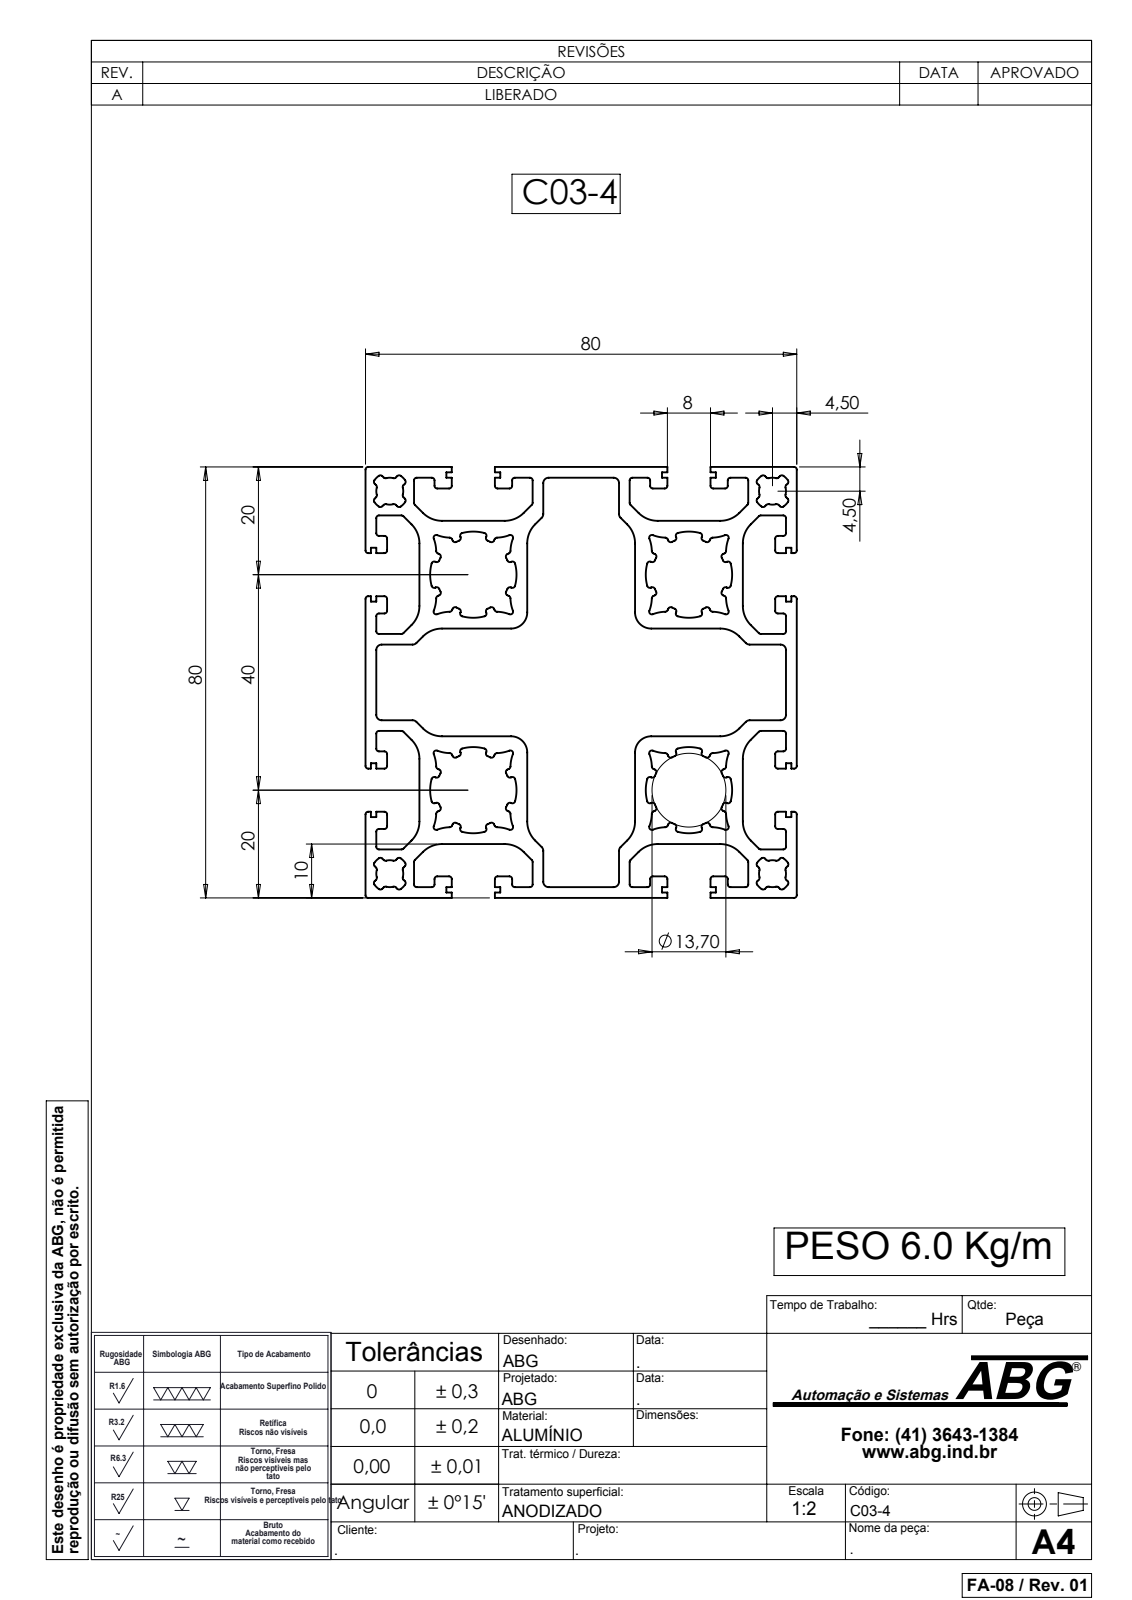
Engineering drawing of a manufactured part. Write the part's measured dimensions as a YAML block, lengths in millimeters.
part_name: "C03-4"
step_written_by: "SolidWorks 2007 (CONFIG_CONTROL_DESIGN)"
units: millimeters
bodies: {solids: 1, faces: 818, planar: 306, cylindrical: 512, other: 0}
overall_size: [6000, 80, 80]
volume: 10040000
surface_area: 8449000
partial_cylinders:
  - {radius: 0.5, count: 300}
  - {radius: 7, count: 32}
  - {radius: 5, count: 24}
  - {radius: 1, count: 16}
  - {radius: 2.5, count: 4}
  - {radius: 3, count: 4}
  - {radius: 3.5, count: 4}
  - {radius: 6.85, count: 4}
face_to_face_distances: [20, 2, 40, 80, 48, 78, 8, 30, 50, 28]
